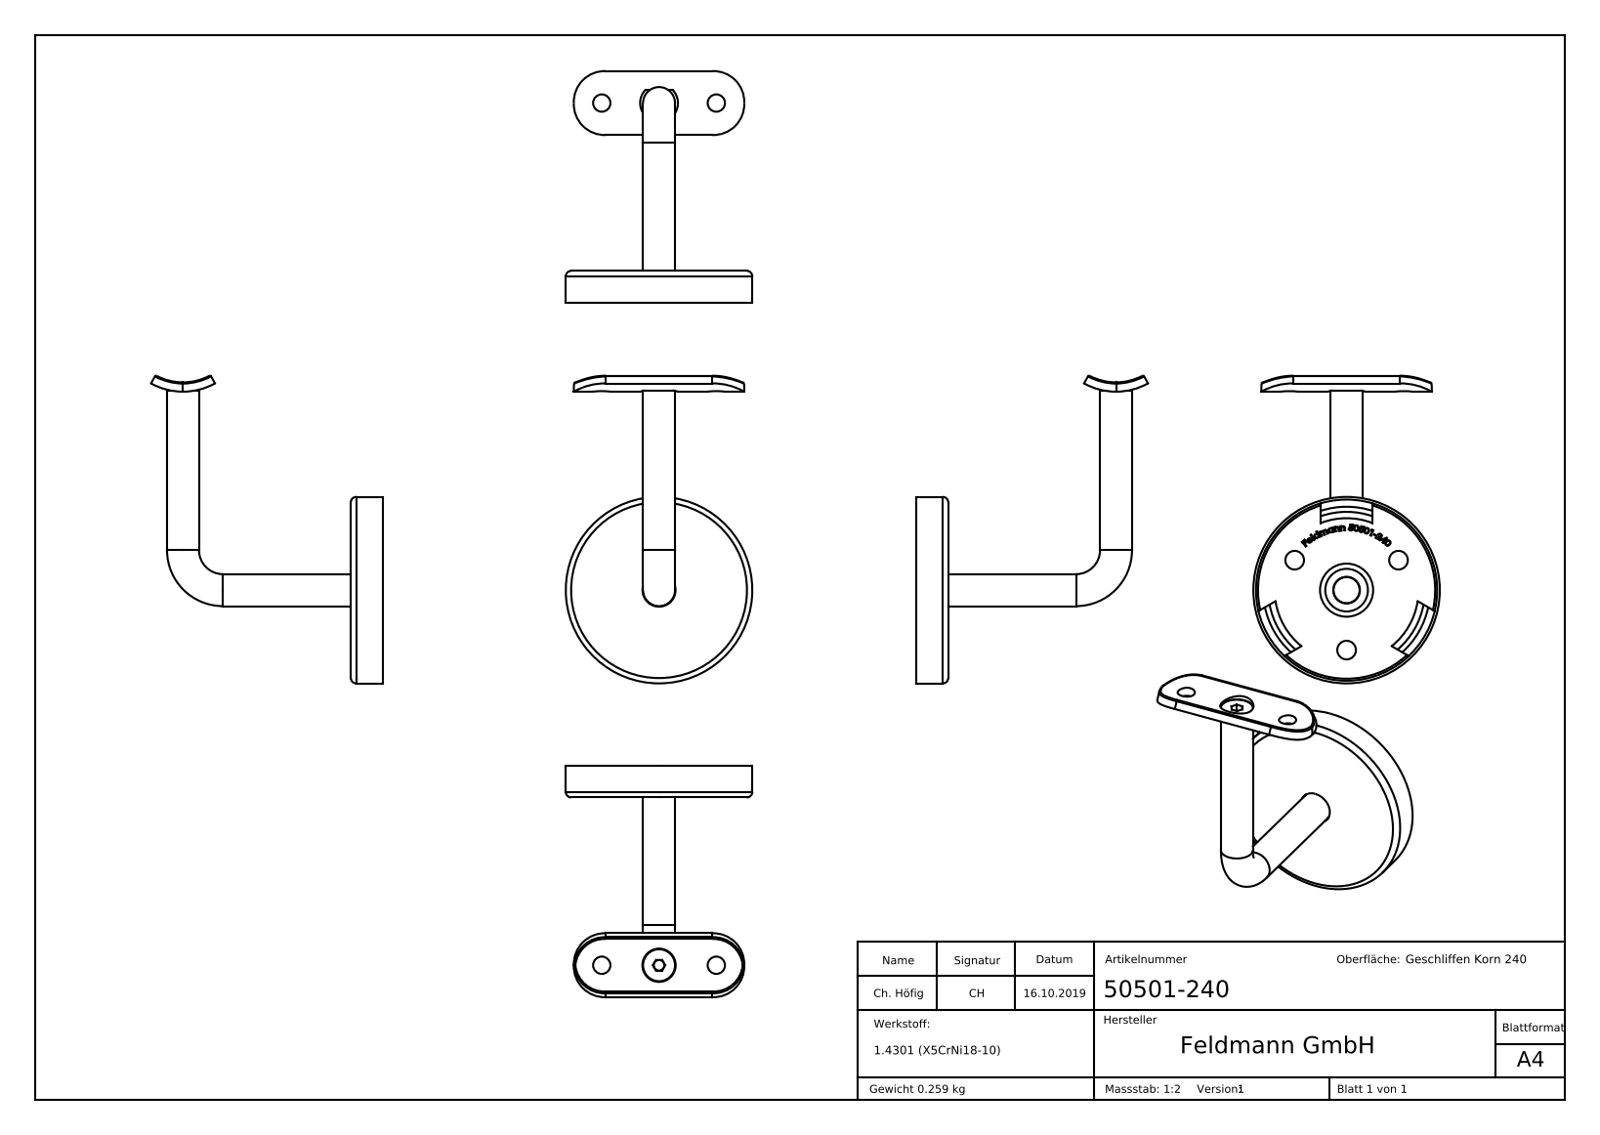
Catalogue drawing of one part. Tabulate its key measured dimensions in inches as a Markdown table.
| quantity | value |
| --- | --- |
| part name | 60182-240_60182-240; 5050X-240 Teil1; 50501-240; 5050X-240 Teil2_50501-240 Teil2 (+7 more) |
| STEP written by | SolidWorks 2015 (CONFIG_CONTROL_DESIGN) |
| units | inches |
| bodies | 5 solids, 332 faces (163 planar, 40 cylindrical, 129 other) |
| overall size | 4.547 × 3.425 × 2.756 |
| volume | 2.004 in³ |
| surface area | 45.72 in² |
| round holes (diameter × count) | 0.276 × 3, 0.256 × 2, 0.197 × 1, 0.323 × 1, 0.394 × 1, 0.488 × 1, 0.492 × 1 |
| round bosses / shafts (diameter × count) | 0.472 × 2, 2.756 × 1, 2.677 × 1, 0.386 × 1, 0.236 × 1 |
| partial cylindrical surfaces (radius × count) | 0.472 × 4, 0.02 × 2, 0.28 × 1, 0.835 × 1, 0.972 × 1, 1.309 × 1 |
| main face-to-face distances | 0.039, 0.472, 0.433, 0.079, 0.354, 0.394, 0.126, 0.205, 0.228, 0.268 |
| hole center spacings | 0.886, 0.846, 1.534, 1.535, 1.693 |
